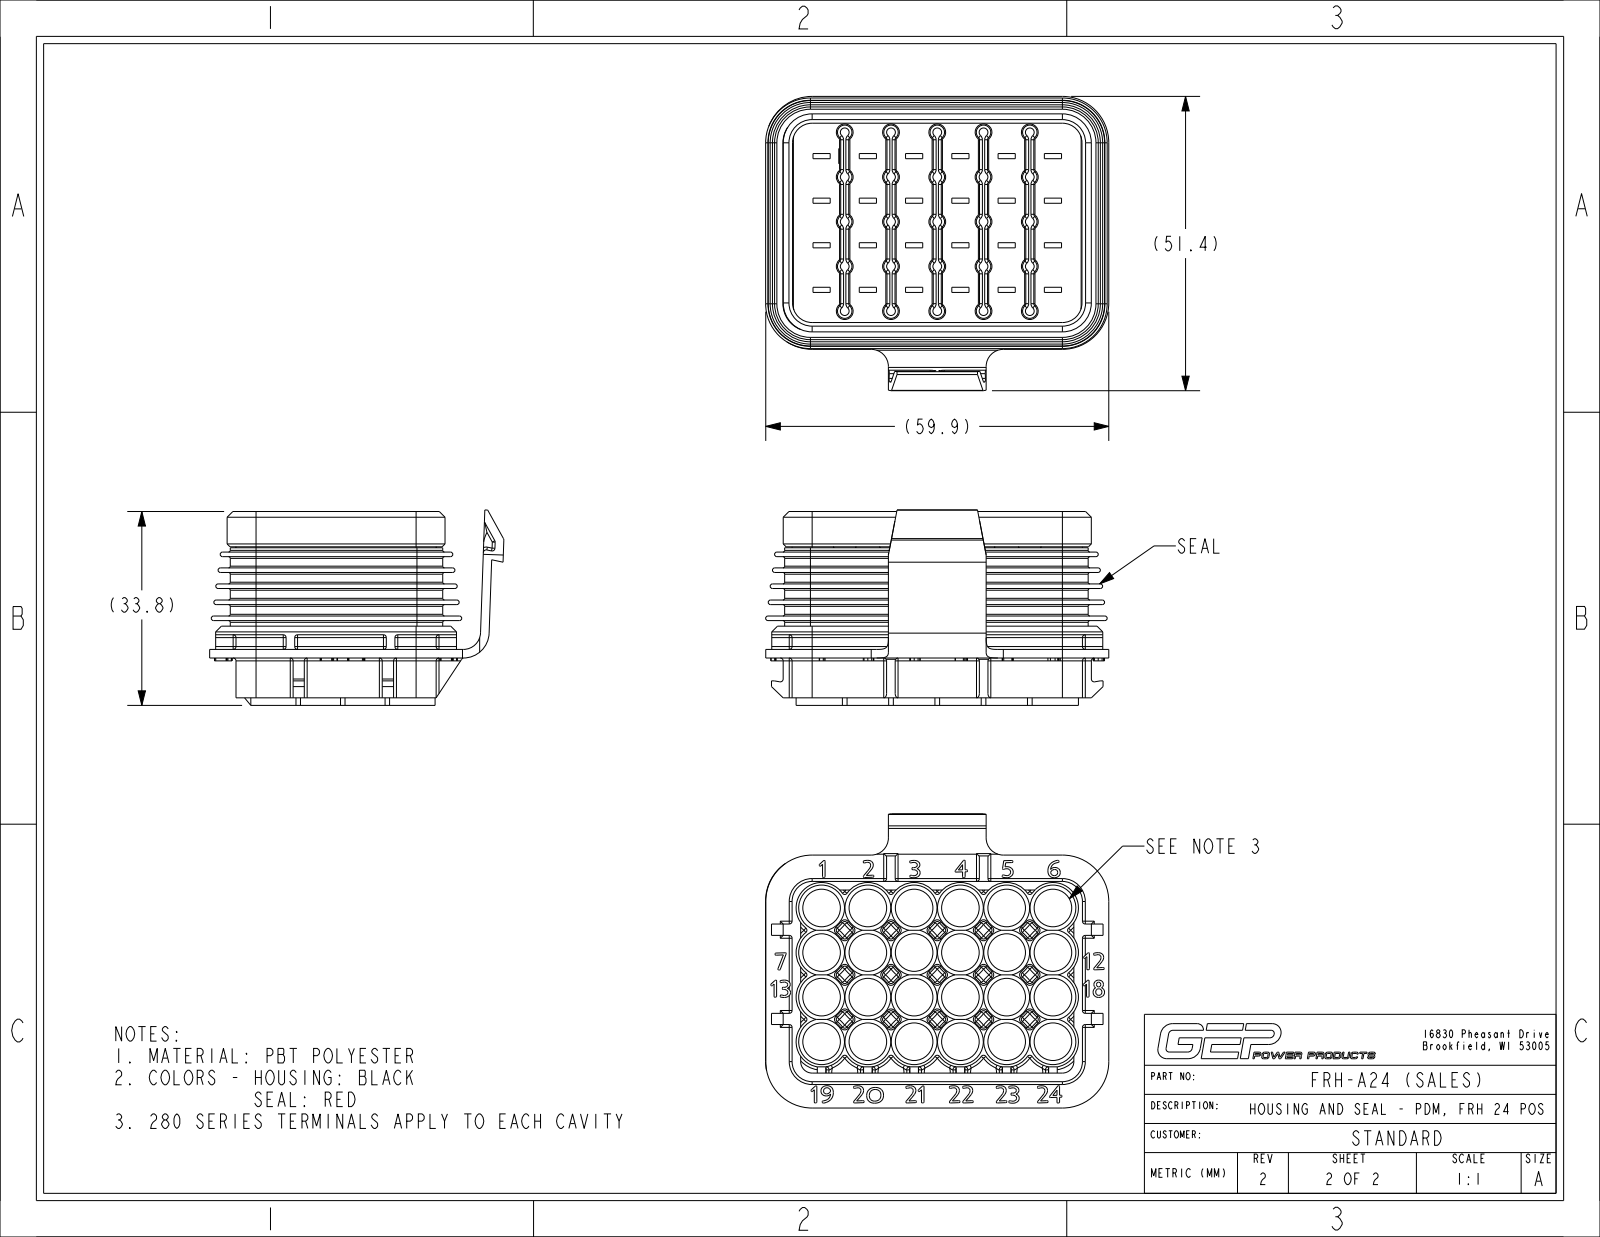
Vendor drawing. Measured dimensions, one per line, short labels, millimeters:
name: FRH-A24-NCF_SALES_REV2
written by: CREO PARAMETRIC BY PTC INC, 2017110 (CONFIG_CONTROL_DESIGN)
unit: mm
bodies: 1 solid, 2541 faces (613 planar, 647 cylindrical, 1281 other)
size: 59.92 × 51.37 × 34.11
volume: 49 397 mm³; area: 33 415 mm²
holes: 24× ⌀6.56
rounds: 248× R0.5, 40× R0.3, 25× R1.26, 24× R4.45, 20× R0.4, 10× R2.77, 8× R6.54, 7× R3
face distances: 1.5, 0.8, 1, 7.78, 23.8, 2.79, 4.06, 33.44, 19.06, 4.74
hole spacings: 11.22, 17.94, 8.08, 17.53, 7.78, 25.46, 16.16, 22.43
